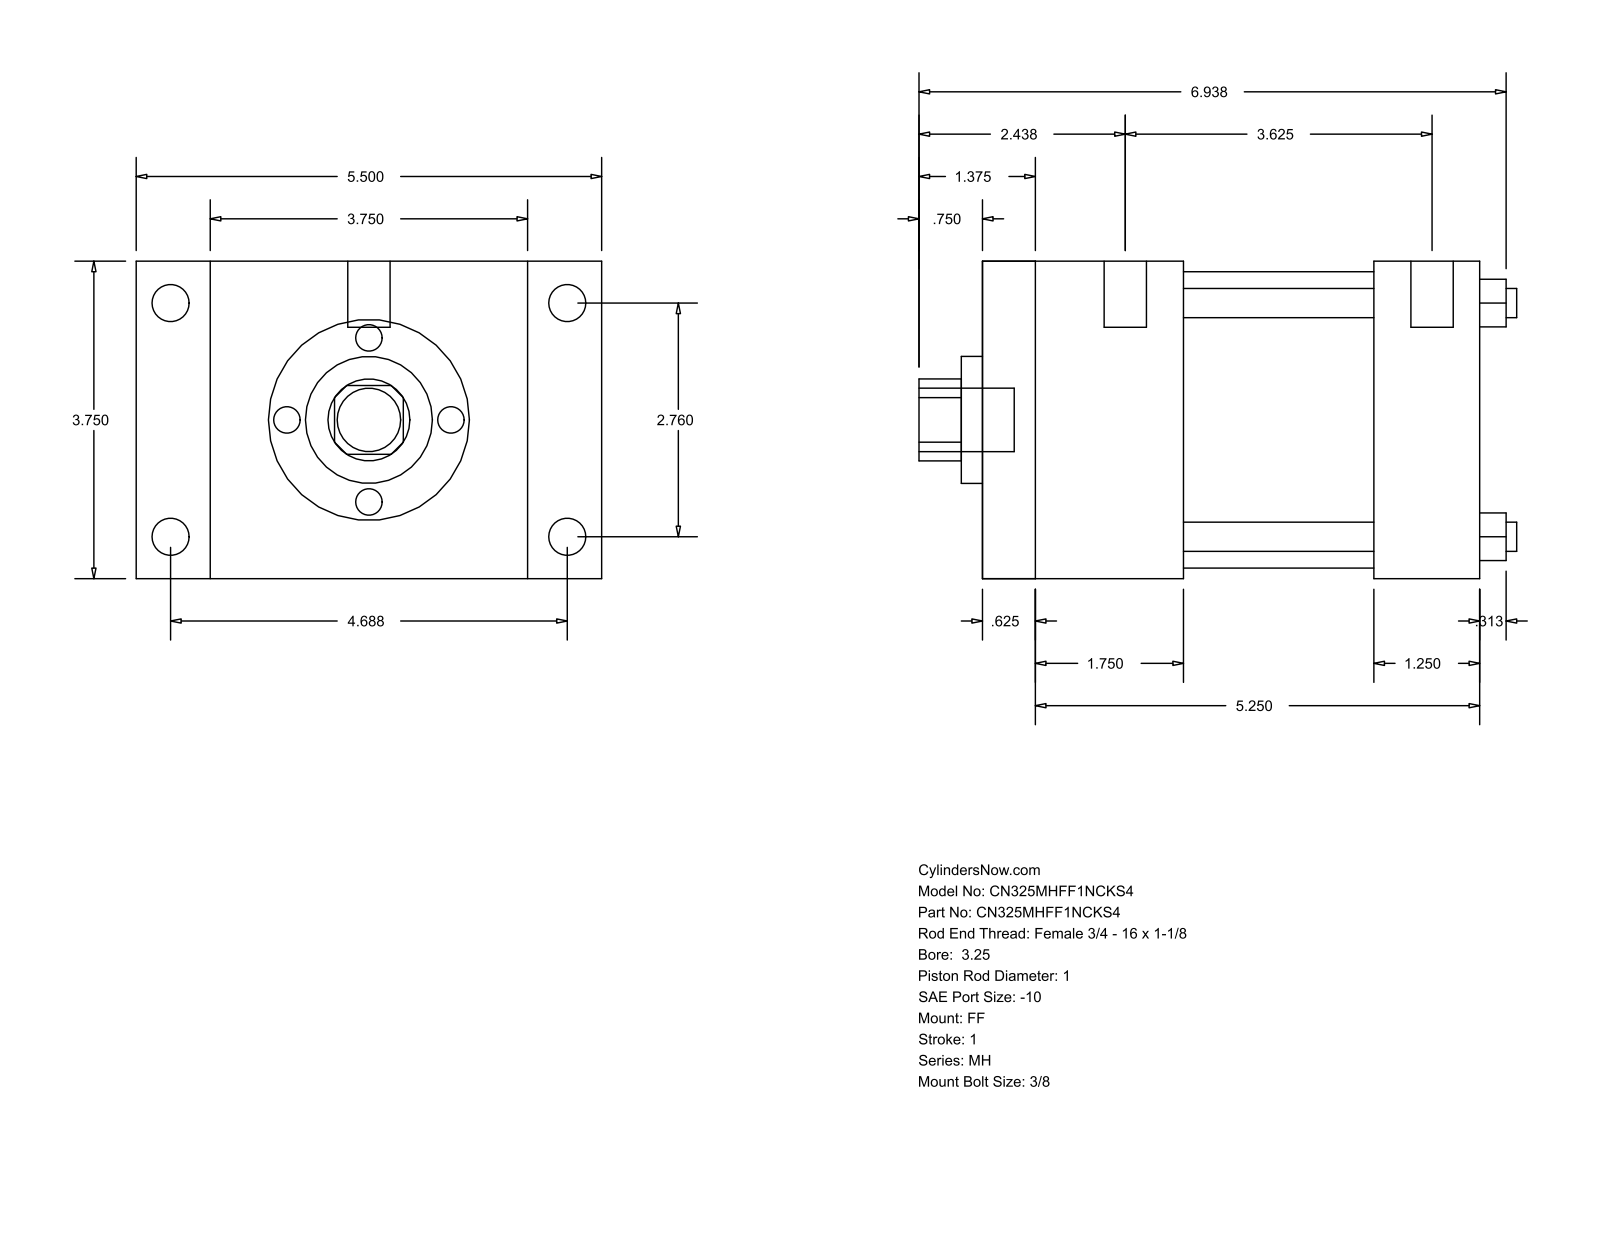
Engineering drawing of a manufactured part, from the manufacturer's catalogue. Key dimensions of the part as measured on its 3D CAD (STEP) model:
Part name (STEP PRODUCT): MH_FF__0325_1
STEP written by: GSSL Pune (CONFIG_CONTROL_DESIGN)
Units: millimetres
Bodies: 0 solids, 92 faces (64 planar, 28 cylindrical, 0 other)
Overall size (bounding box): 179.39 × 139.7 × 95.25
Round holes (diameter × count): ⌀8.76 ×4, ⌀25.4 ×1, ⌀38.1 ×1, ⌀88.9 ×1
Round bosses / shafts (diameter × count): ⌀11.13 ×4, ⌀5.56 ×4, ⌀12.7 ×2, ⌀19.05 ×1
Partial cylindrical surfaces — rounded edges, fillets, slot ends (radius × count): R12.29 ×1
Main face-to-face distances: 95.24, 149.23, 15.87, 133.36, 22.23, 117.47, 117.48, 101.61, 31.75, 60.33
Hole centre spacings: 49.57, 70.1, 99.14
